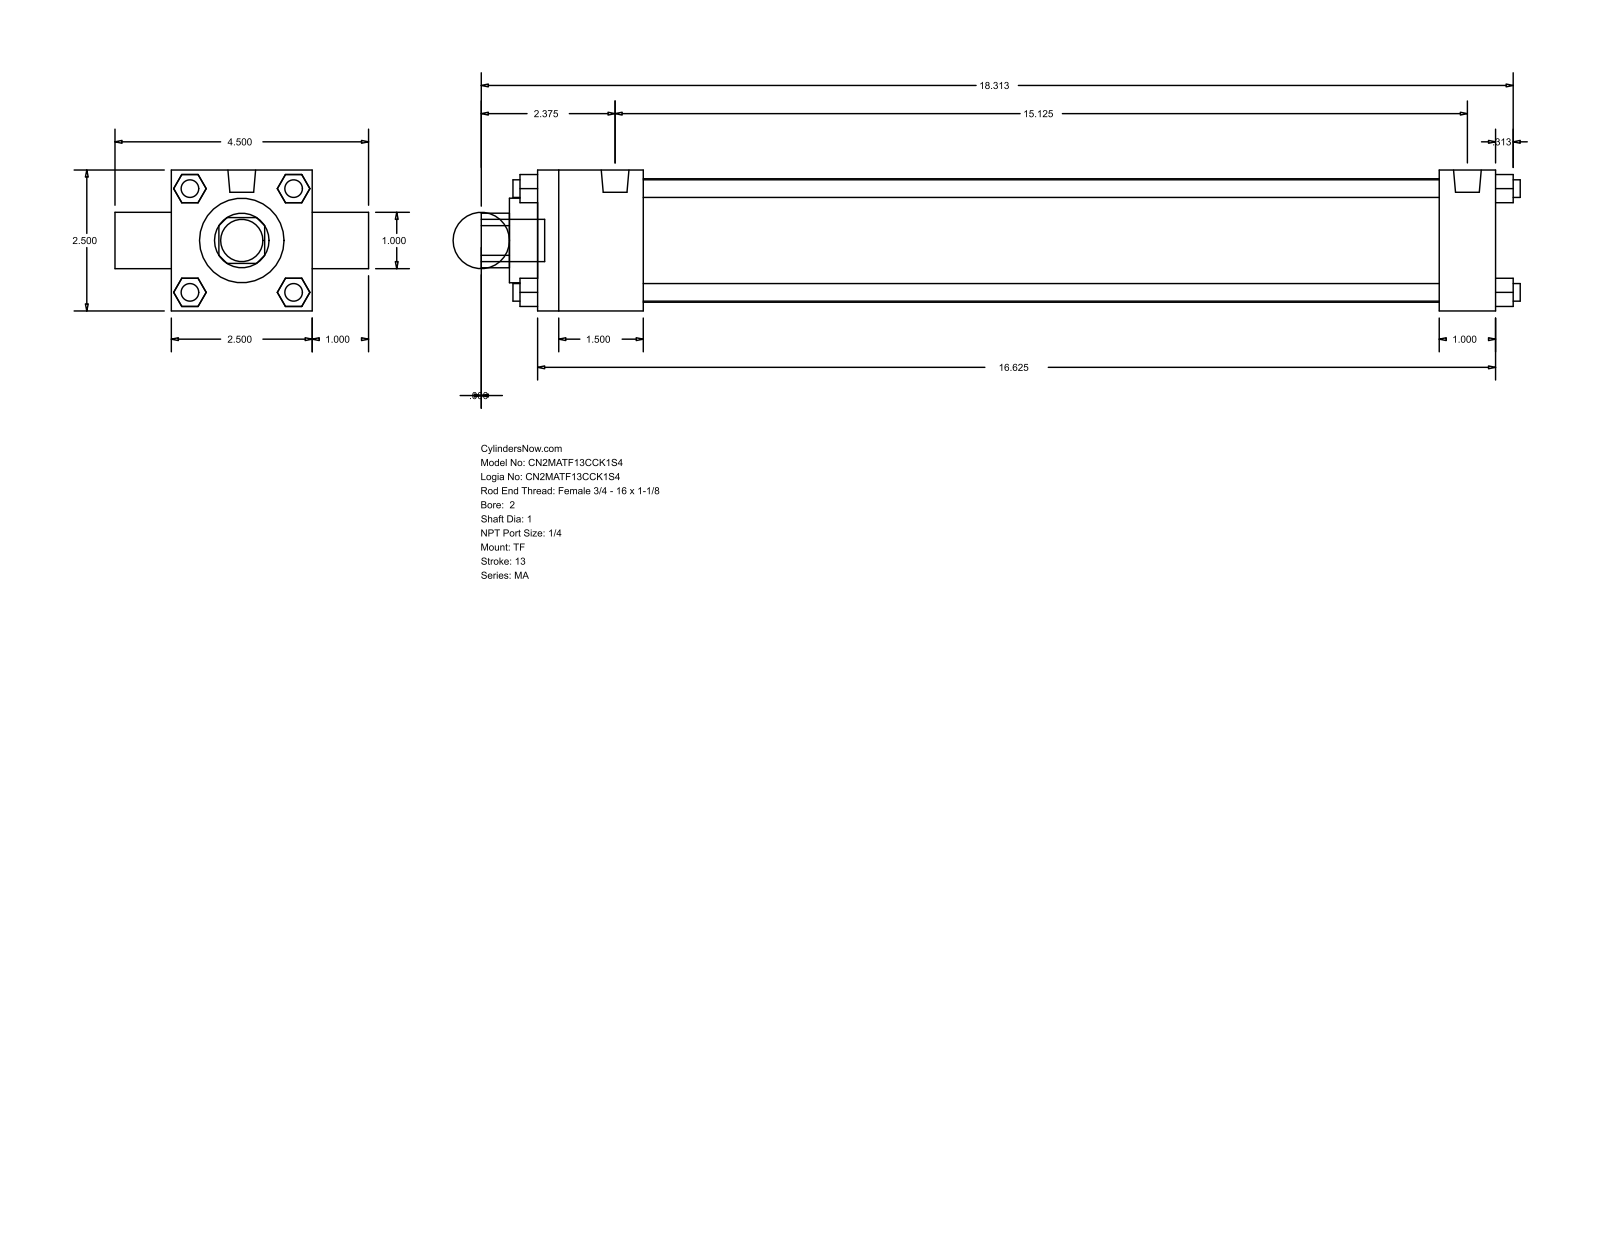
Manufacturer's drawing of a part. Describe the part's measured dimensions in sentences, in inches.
The part is named "MA_TF__0200_1". Its 3-D file was written by "GSSL Pune (CONFIG_CONTROL_DESIGN)". It is 0 solids with 120 faces: 92 planar, 28 cylindrical and 0 other. Overall it measures 18.437 by 4.5 by 2.5 inches. Round holes: 2 of diameter 1, 1 of diameter 1.5, 1 of diameter 2.19. Round bosses or shafts: 7 of diameter 0.313, 2 of diameter 0.492, 1 of diameter 0.75. Partial cylindrical surfaces (rounded edges, fillets, slot ends): 1 of radius 0.484. The main face-to-face distances are 2.5, 1, 17, 0.5, 1.875, 16, 14.125, 15.125, 3.5, 1.593.
